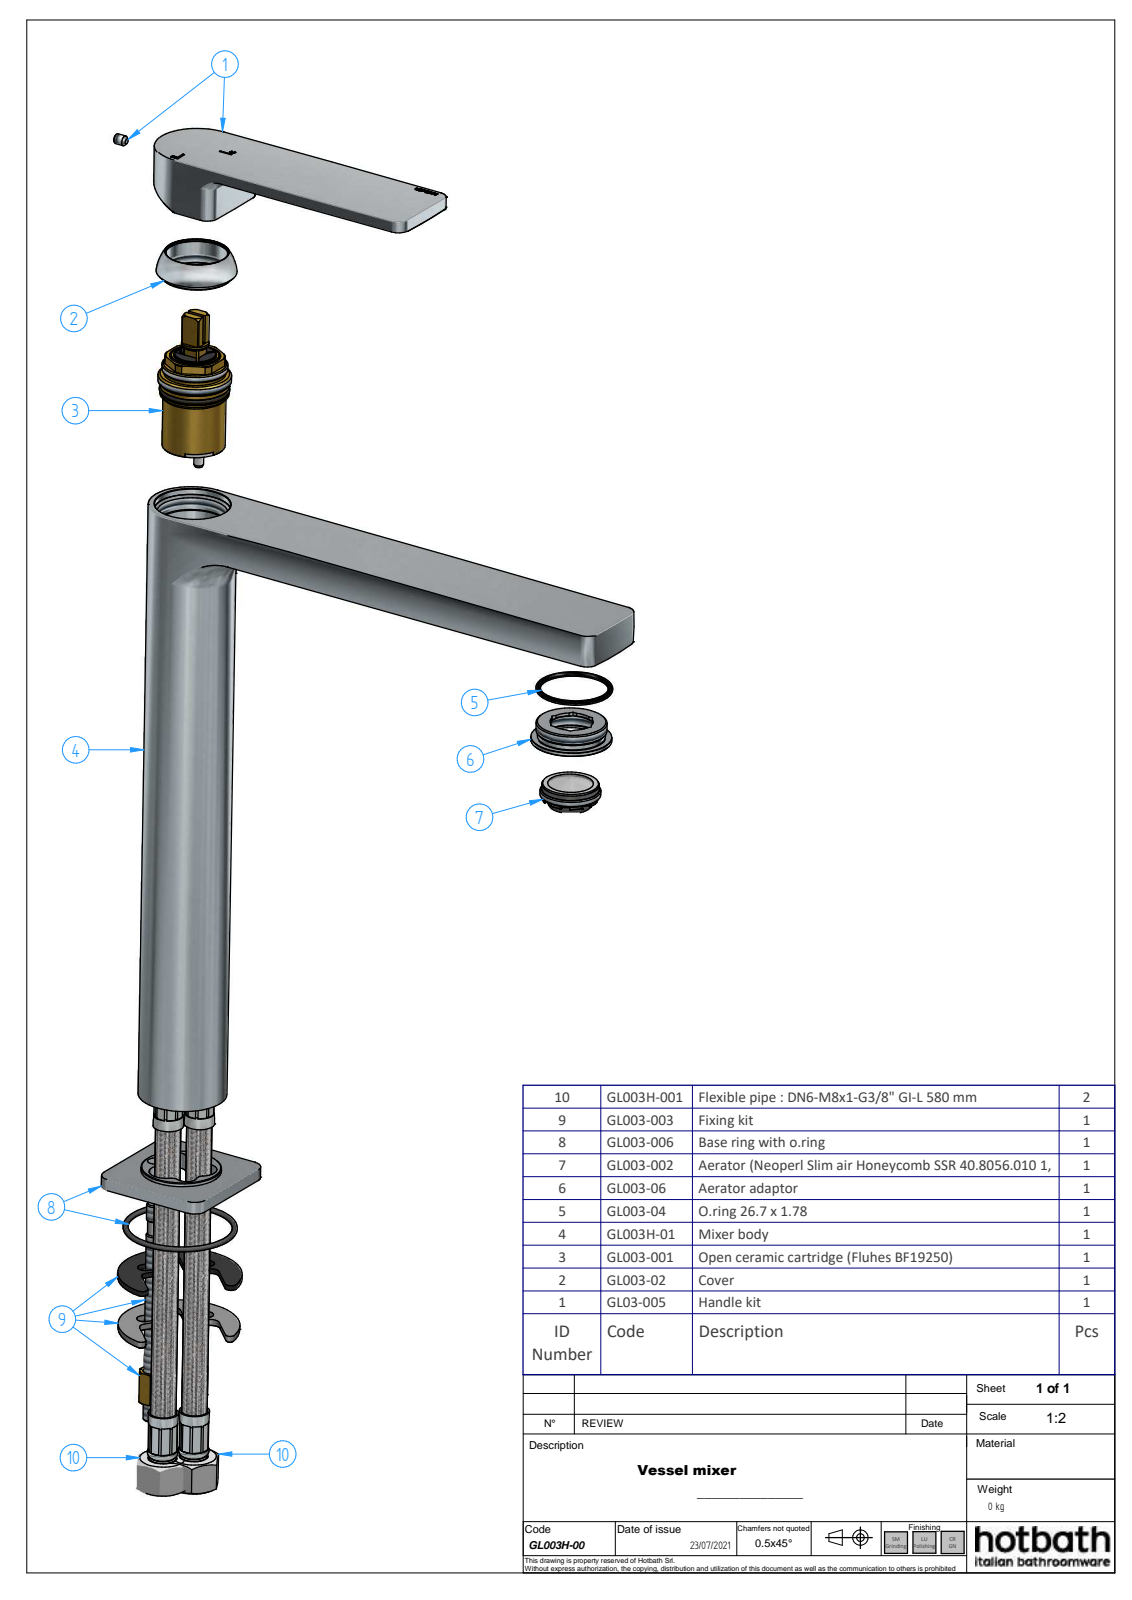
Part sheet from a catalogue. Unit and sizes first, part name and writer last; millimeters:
Units: millimetres
Overall size (bounding box): 282.94 × 223.5 × 48
Round holes (diameter × count): ⌀4 ×3, ⌀5.6 ×3, ⌀4.92 ×2, ⌀5.5 ×2, ⌀6 ×2, ⌀6.92 ×2, ⌀7.8 ×2, ⌀9 ×2, ⌀12 ×2, ⌀3.24 ×1, ⌀4.2 ×1, ⌀15.8 ×1
Round bosses / shafts (diameter × count): ⌀3.85 ×3, ⌀35 ×1, ⌀32 ×1, ⌀31.7 ×1, ⌀28.5 ×1, ⌀28 ×1, ⌀27.2 ×1, ⌀26.8 ×1
Partial cylindrical surfaces — rounded edges, fillets, slot ends (radius × count): R0.1 ×32, R0.5 ×22, R2.5 ×14, R0.2 ×13, R0.75 ×12, R1 ×10, R2 ×10, R5 ×10
Main face-to-face distances: 1.5, 5, 243.04, 3.5, 248.04, 6.5, 244.54, 0.8, 246.54, 12.88
Hole centre spacings: 9.5, 1.53, 1.57, 3.18, 6.11, 6.21, 6.71, 7.16
Volume: 170 960 mm³ · Surface area: 121 539 mm²
Bodies: 12 solids, 1167 faces (320 planar, 338 cylindrical, 509 other)
Part name (STEP PRODUCT): GL003H-00; GL003-02; GL003-05; GL003-09 (+8 more)
STEP written by: ST-DEVELOPER v16.7 (AUTOMOTIVE_DESIGN)
